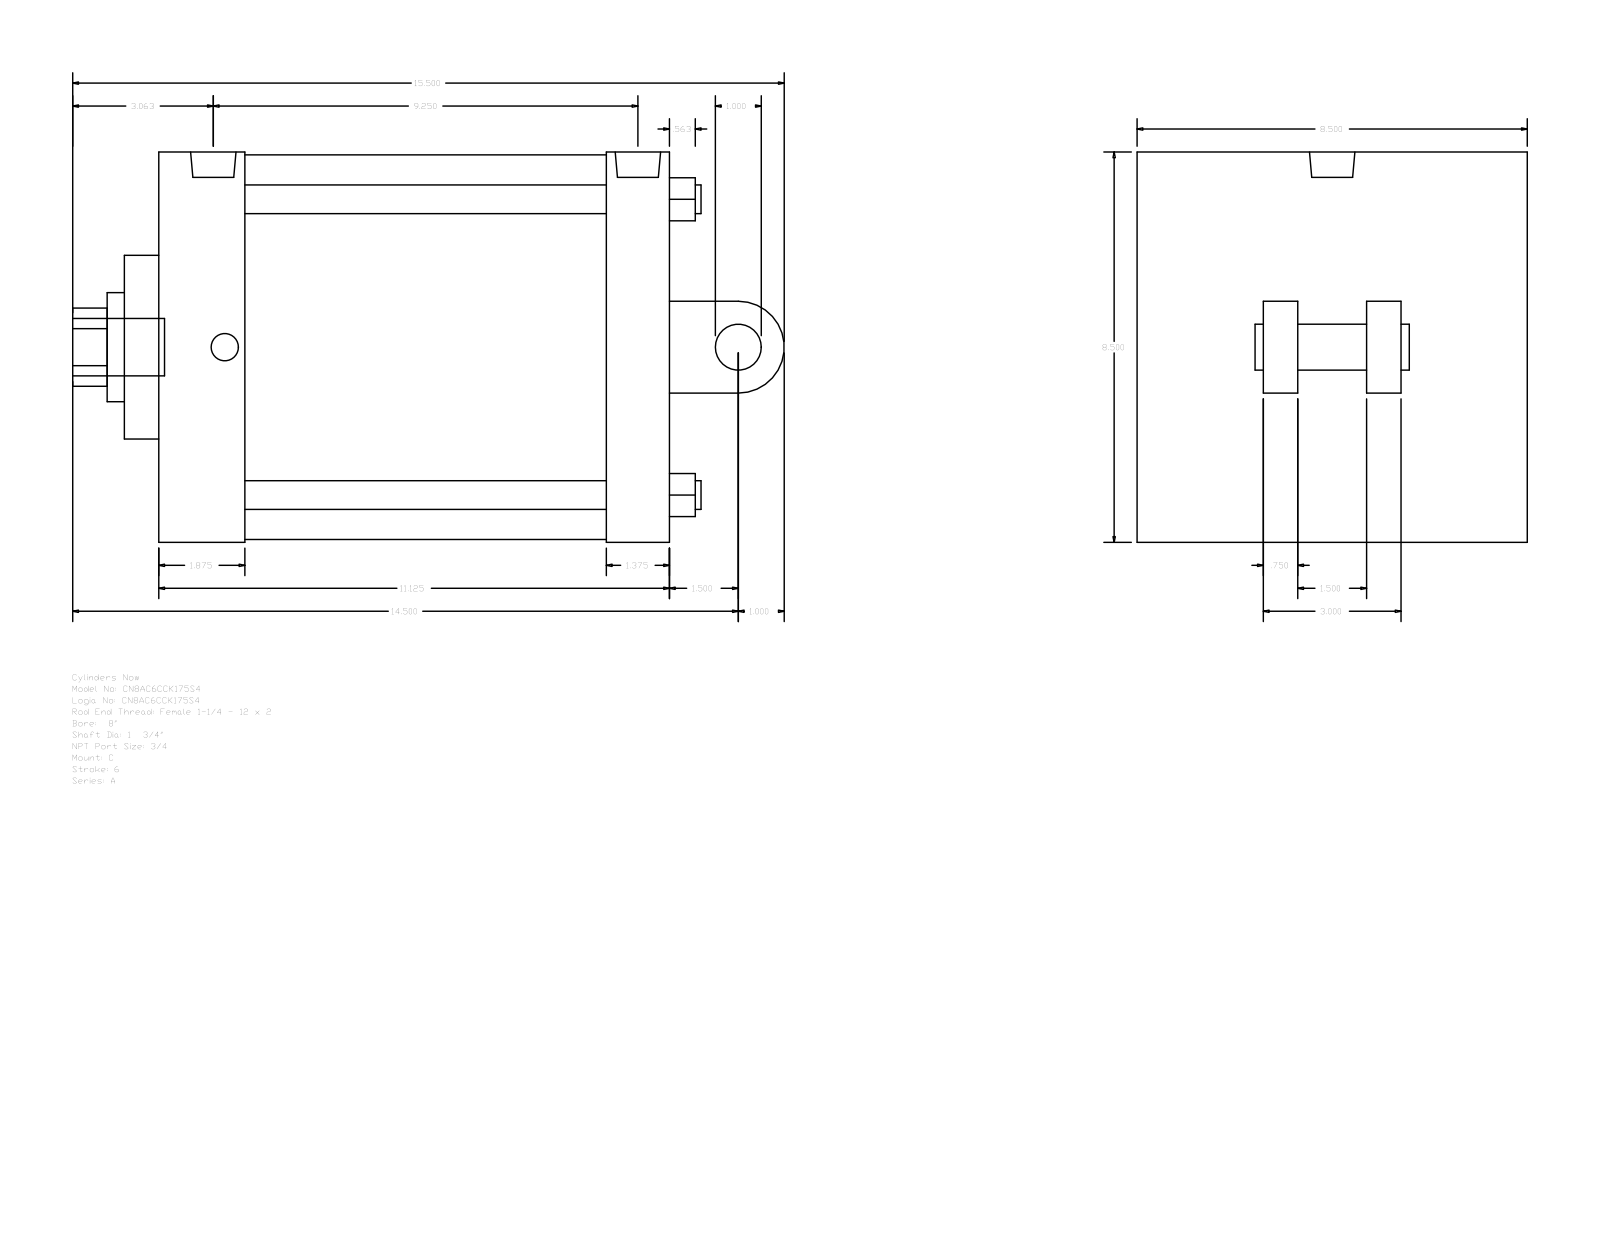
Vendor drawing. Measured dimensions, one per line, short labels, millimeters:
name: A_C__0800_1.75
written by: GSSL Pune (CONFIG_CONTROL_DESIGN)
unit: mm
bodies: 0 solids, 104 faces (75 planar, 29 cylindrical, 0 other)
size: 393.7 × 215.9 × 215.9
holes: 4× ⌀15.88, 2× ⌀15.08, 1× ⌀25.12, 1× ⌀44.45, 1× ⌀60.33, 1× ⌀212.72
bosses: 2× ⌀15.08, 1× ⌀31.75, 1× ⌀25.4, 1× ⌀25.12
rounds: 1× R21.63, 1× R25.4
face distances: 282.58, 215.9, 19.05, 57.15, 47.63, 234.95, 247.65, 200.02, 34.93, 88.9
hole spacings: 115.67, 163.58, 231.34, 6.35
